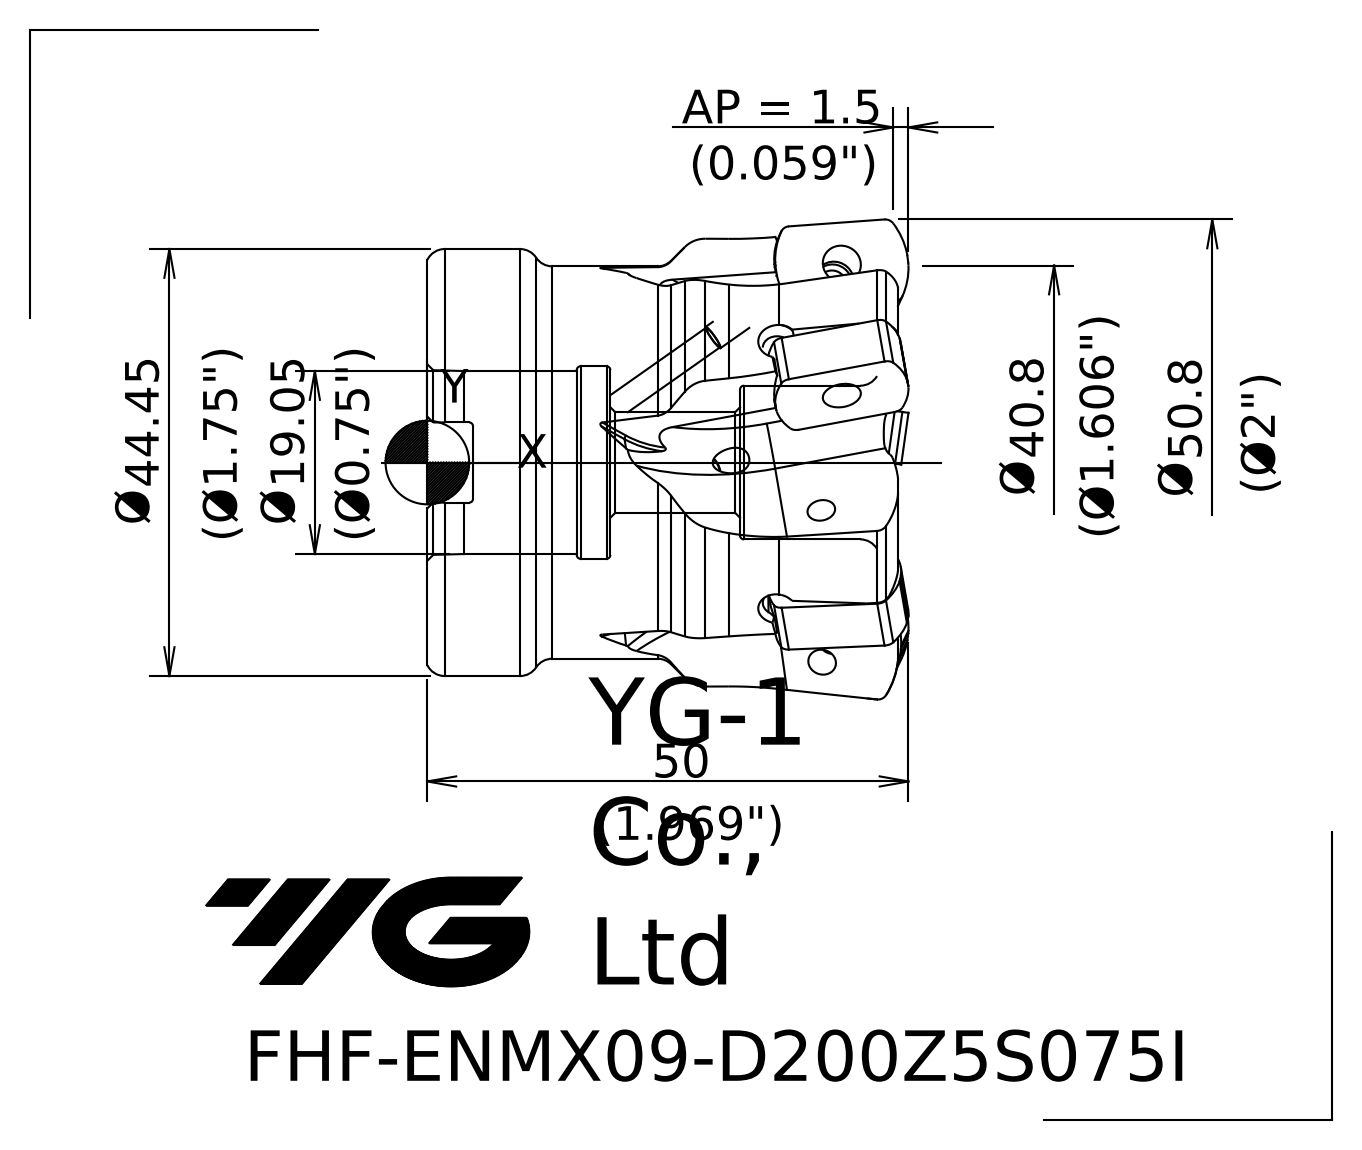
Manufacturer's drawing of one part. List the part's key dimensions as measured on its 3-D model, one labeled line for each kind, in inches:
Part name (STEP PRODUCT): 120185C07CB1h834
STEP written by: SIEMENS PLM Software NX 10.0 (AP203_CONFIGURATION_CONTROLLED_3D_DESIGN_OF_MECHANICAL_PARTS_AND_ASSEMBLIES_MIM_LF)
Units: inches
Bodies: 1 solid, 73 faces (17 planar, 11 cylindrical, 45 other)
Overall size (bounding box): 2 × 2 × 1.969
Volume: 4.218 in³ · Surface area: 19.91 in²
Round holes (diameter × count): ⌀0.413 ×1, ⌀0.63 ×1, ⌀0.75 ×1, ⌀0.789 ×1
Round bosses / shafts (diameter × count): ⌀1.836 ×1, ⌀1.75 ×1, ⌀1.608 ×1
Partial cylindrical surfaces — rounded edges, fillets, slot ends (radius × count): R0.016 ×2
Main face-to-face distances: 1.834, 0.394, 1.441, 1.647, 1.254, 0.187, 1.084, 0.691, 0.563, 0.75
